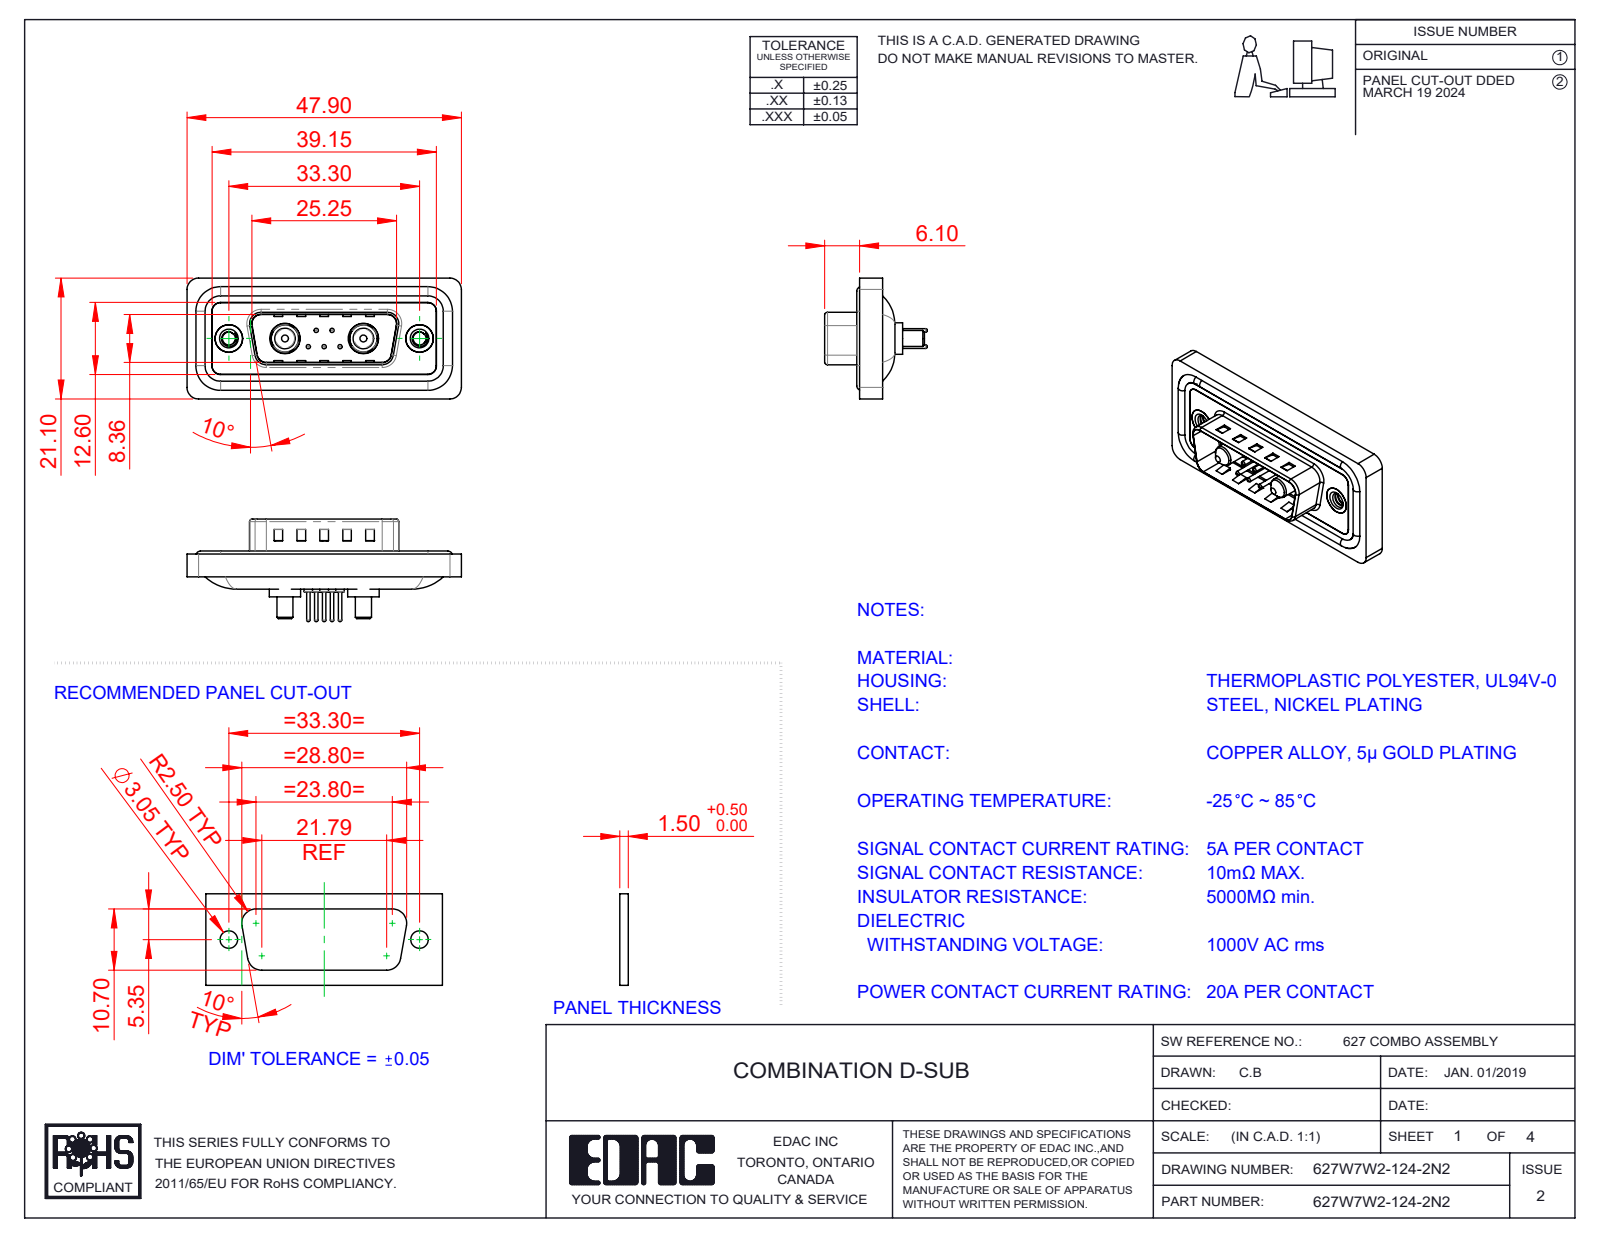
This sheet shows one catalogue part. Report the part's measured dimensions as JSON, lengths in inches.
{"part_name": "627Combo Housing_7W2; 627Combo Contact Row 2_24; 627Combo Waterproof Housing_15 Contacts; 627Combo Threaded Rivet_2 (+5 more)", "step_written_by": "SolidWorks 2023 (CONFIG_CONTROL_DESIGN)", "units": "inches", "bodies": {"solids": 16, "faces": 710, "planar": 232, "cylindrical": 292, "other": 186}, "overall_size": [1.886, 0.831, 0.705], "volume_in3": 0.337, "surface_area_in2": 13.63, "round_holes": [[0.03, 5], [0.063, 5], [0.079, 5], [0.089, 2], [0.157, 2], [0.189, 2], [0.191, 2], [0.197, 2], [0.209, 2]], "round_bosses_or_shafts": [[0.059, 5], [0.024, 5], [0.063, 4], [0.217, 2], [0.205, 2], [0.193, 2], [0.187, 2], [0.148, 2]], "partial_cylinders_radius": [[0.059, 26], [0.079, 20], [0.02, 8], [0.063, 8], [0.01, 4], [0.024, 4], [0.026, 4], [0.035, 4]], "face_to_face_distances": [0.016, 0.043, 0.059, 0.063, 0.02, 0.122, 0.114, 0.032, 0.377, 0.157], "hole_center_spacings": [0.124, 0.109, 0.386, 0.925, 0.17, 0.17, 0.198, 0.198]}
